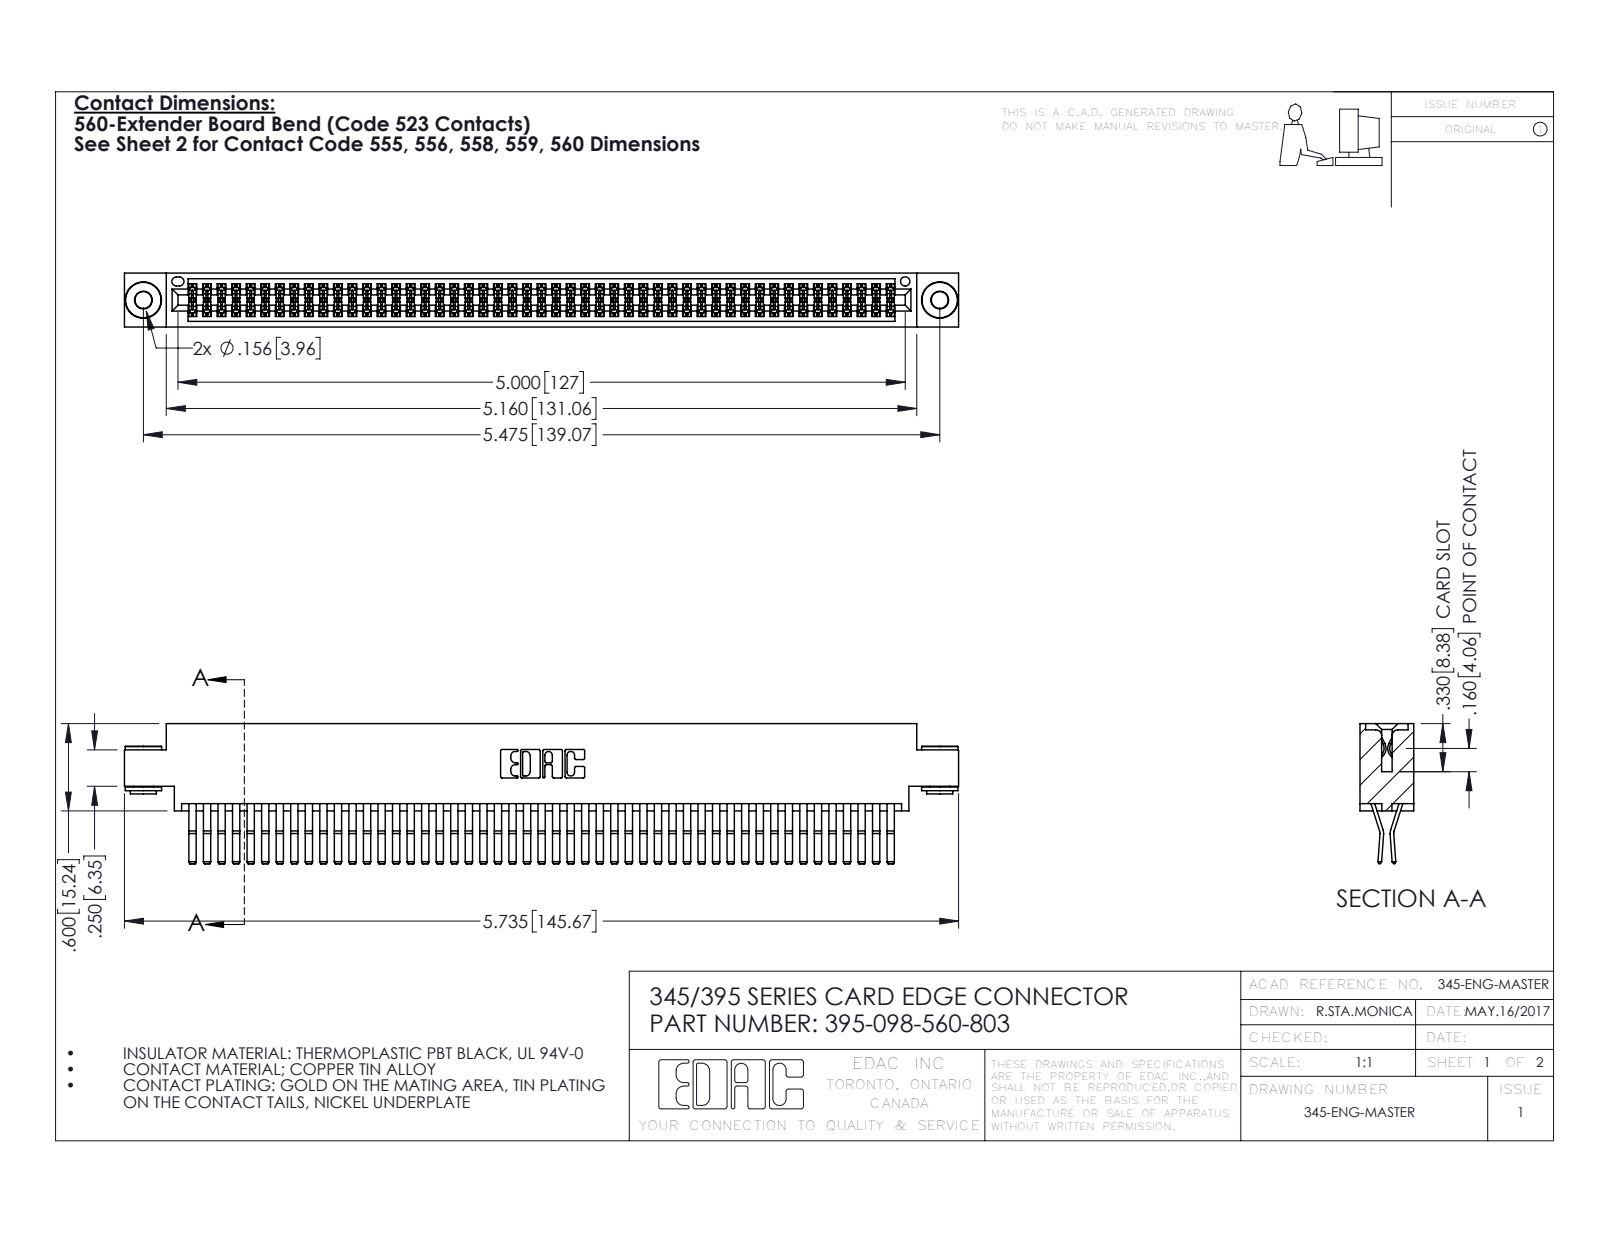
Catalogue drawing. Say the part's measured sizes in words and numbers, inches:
The part is named "345-292-001_560 Tail; 395-098-560-803; 345-250-002_345-250-002-102; 345 Part_0.170 Offset - 0.156 Dia-TH". Its 3-D file was written by "SolidWorks 2016 (CONFIG_CONTROL_DESIGN)". It is 101 solids with 5264 faces: 3328 planar, 1928 cylindrical and 8 other. Overall it measures 5.735 by 0.962 by 0.37 inches. Its volume is 0.901 cubic inches and its surface area 37.14 square inches. Round holes: 2 of diameter 0.116, 2 of diameter 0.156, 1 of diameter 0.064. Round bosses or shafts: 2 of diameter 0.25, 2 of diameter 0.18, 2 of diameter 0.136. Partial cylindrical surfaces (rounded edges, fillets, slot ends): 147 of radius 0.006, 22 of radius 0.01, 6 of radius 0.007, 6 of radius 0.031, 3 of radius 0.026, 2 of radius 0.01, 2 of radius 0.014, 2 of radius 0.019. The main face-to-face distances are 0.025, 0.072, 0.298, 0.37, 0.2, 0.098, 0.272, 0.225, 0.175, 0.149. The hole center spacings are 0.27, 5.239, 5.475.
